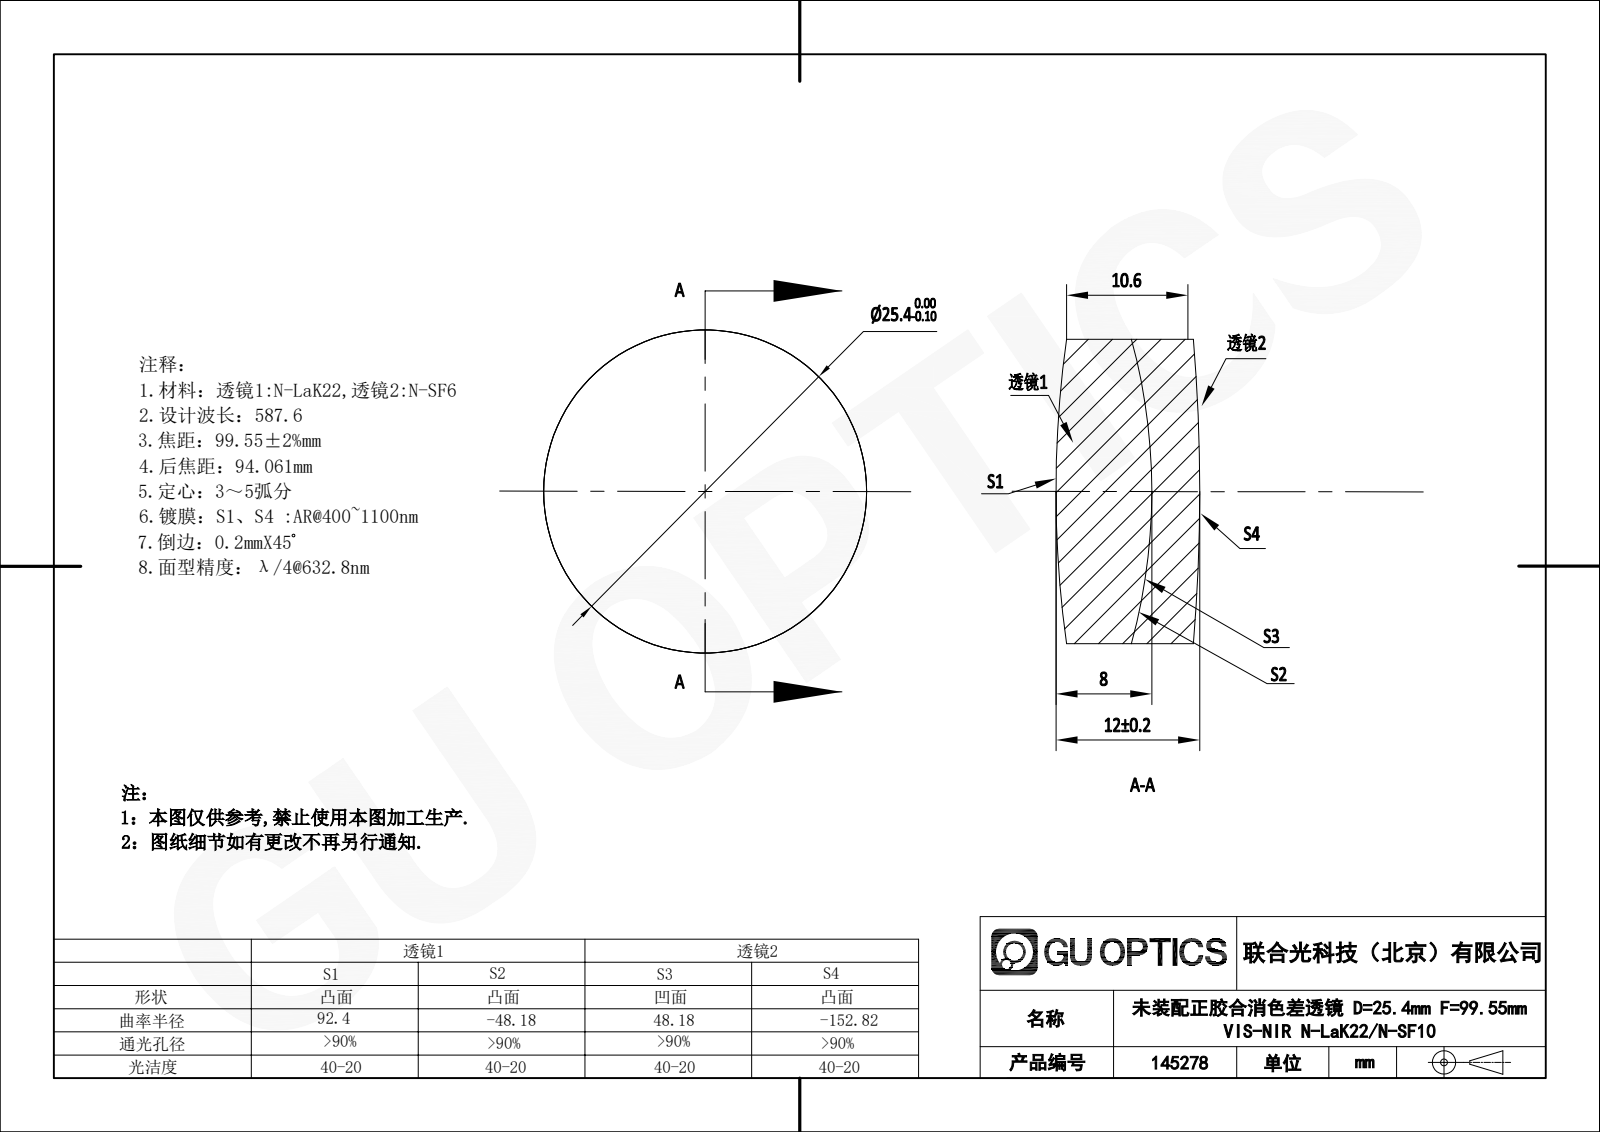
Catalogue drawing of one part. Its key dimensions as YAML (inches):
part_name: "145278"
step_written_by: "SolidWorks 2020 (CONFIG_CONTROL_DESIGN)"
units: inches
bodies: {solids: 2, faces: 12, planar: 0, cylindrical: 4, other: 8}
overall_size: [1, 1, 0.472]
volume: 0.349
surface_area: 4.486
round_bosses_or_shafts:
  - {diameter: 1, count: 1}
